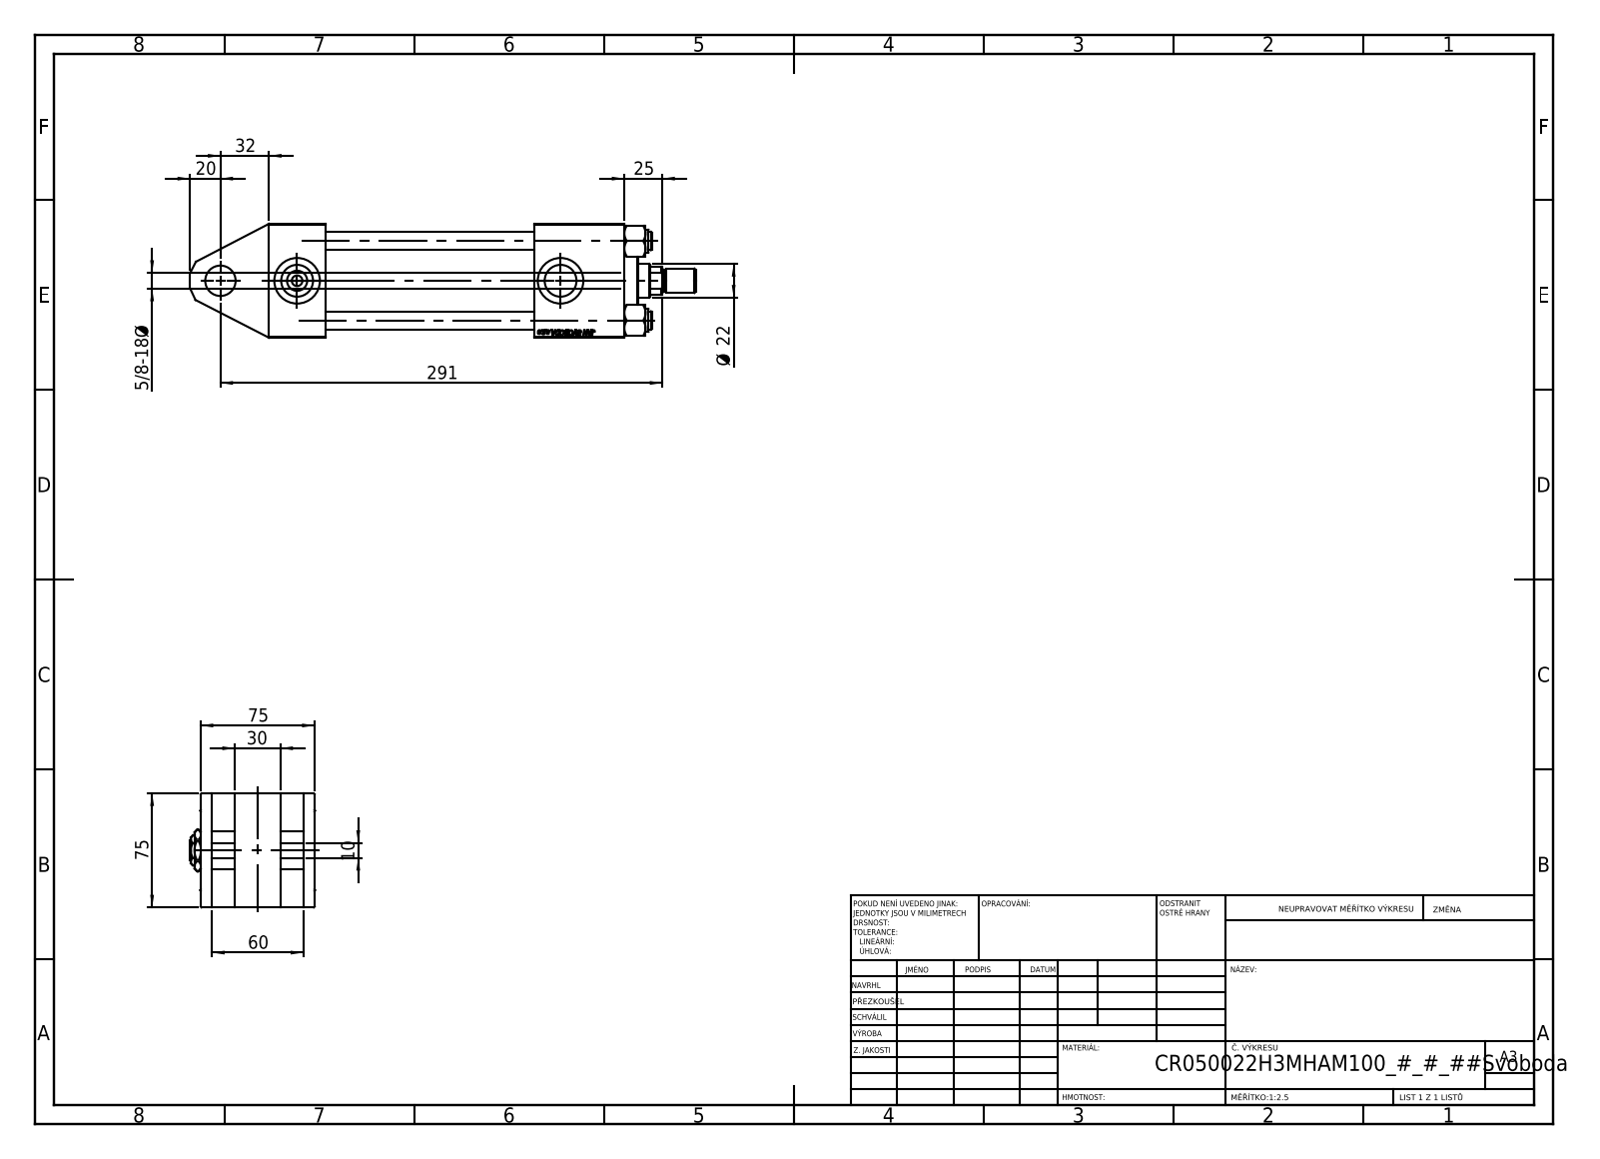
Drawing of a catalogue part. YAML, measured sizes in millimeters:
part_name: "Zatka_pro_OIL_PORT; V215CR_H_Body; V215CR_TYCINKA_H; V215_VC_A (+3 more)"
step_written_by: "SolidWorks 2019 (CONFIG_CONTROL_DESIGN)"
units: millimeters
bodies: {solids: 14, faces: 1243, planar: 569, cylindrical: 98, other: 576}
overall_size: [333, 82.27, 75]
volume: 839430
surface_area: 213226
round_holes:
  - {diameter: 12, count: 4}
  - {diameter: 7, count: 2}
  - {diameter: 20.96, count: 2}
  - {diameter: 30, count: 2}
  - {diameter: 10.5, count: 1}
  - {diameter: 20, count: 1}
  - {diameter: 22, count: 1}
  - {diameter: 25, count: 1}
  - {diameter: 41, count: 1}
  - {diameter: 50, count: 1}
  - {diameter: 53, count: 1}
round_bosses_or_shafts:
  - {diameter: 15, count: 4}
  - {diameter: 56, count: 1}
  - {diameter: 34, count: 1}
  - {diameter: 16, count: 1}
  - {diameter: 14, count: 1}
partial_cylinders:
  - {radius: 10.5, count: 1}
face_to_face_distances: [75, 197, 7.5, 67.5, 45, 22.5, 52.5, 15, 175, 59]
hole_center_spacings: [36.98, 52.3, 73.96, 50.5, 173.5, 224]
